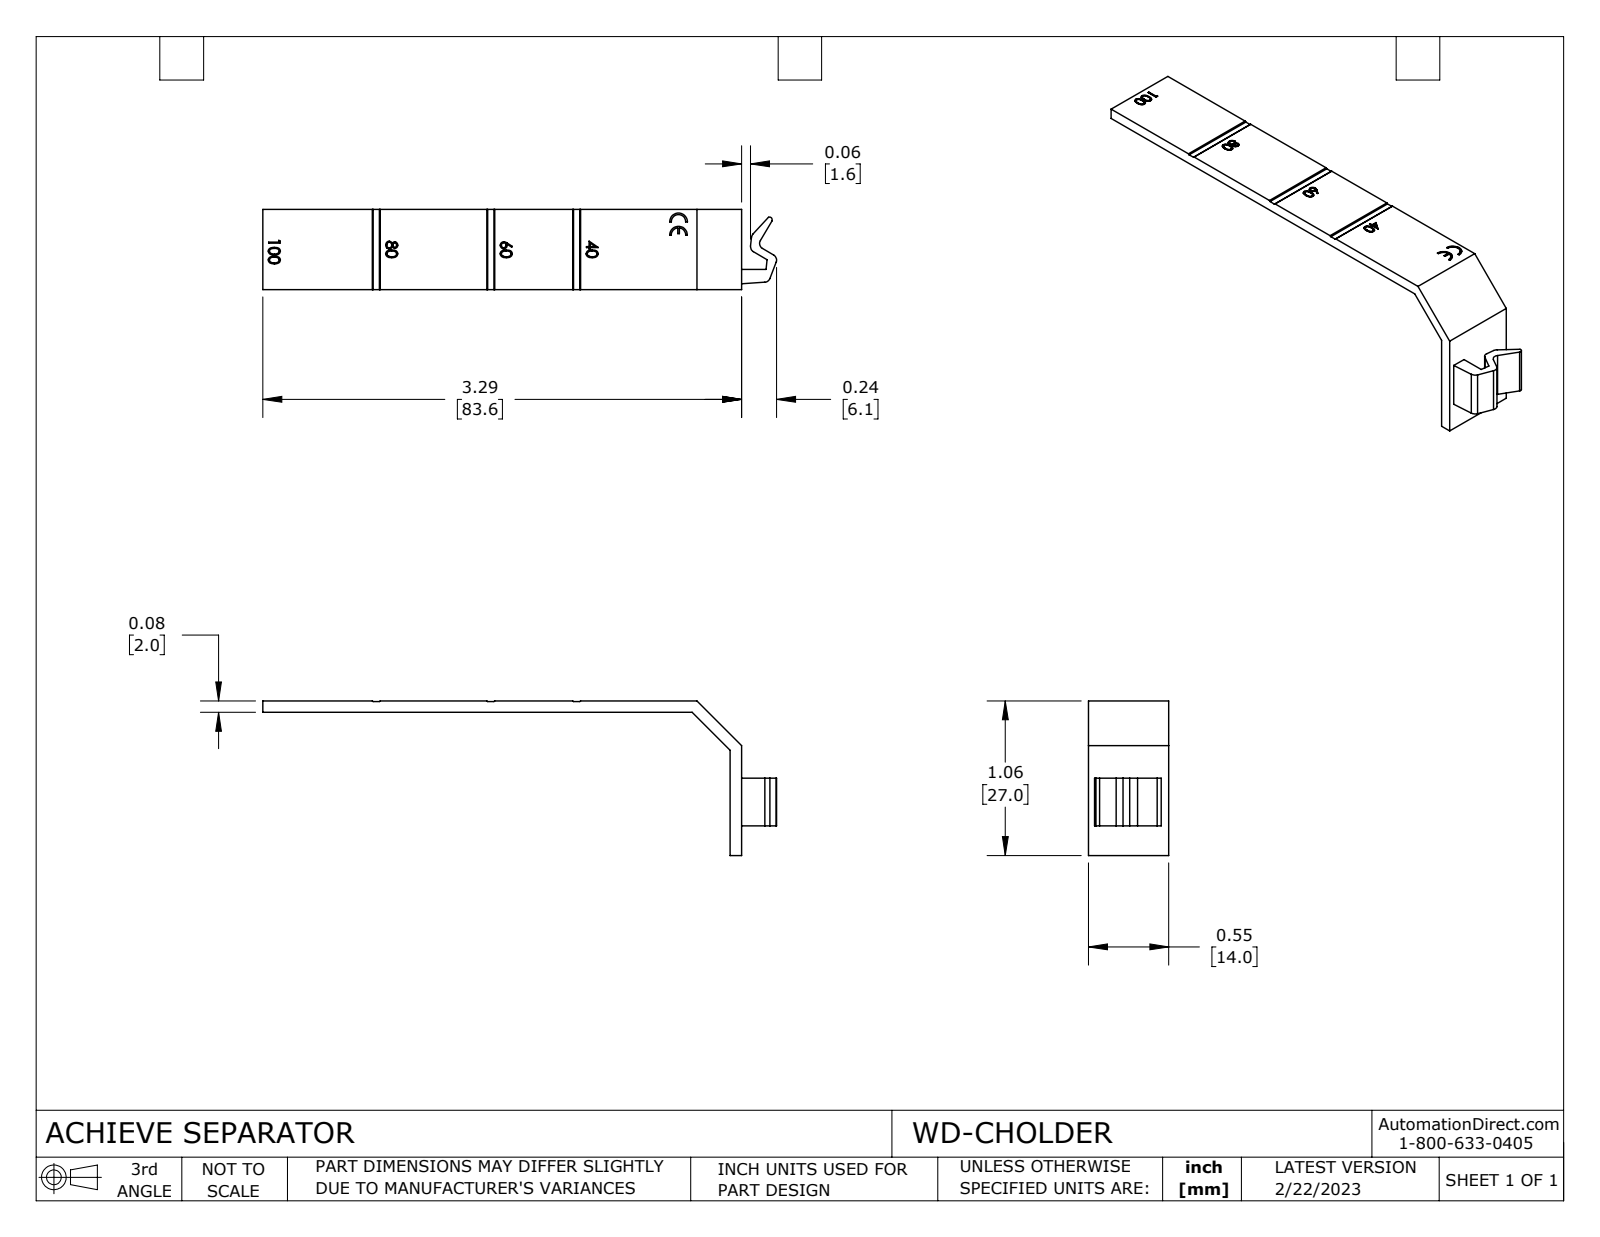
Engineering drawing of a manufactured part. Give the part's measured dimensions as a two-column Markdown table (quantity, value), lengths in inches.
| quantity | value |
| --- | --- |
| part name | WD-CHOLDER |
| STEP written by | SolidWorks 2021 (CONFIG_CONTROL_DESIGN) |
| units | inches |
| bodies | 1 solid, 164 faces (82 planar, 11 cylindrical, 71 other) |
| overall size | 3.532 × 1.063 × 0.551 |
| volume | 0.192 in³ |
| surface area | 5.784 in² |
| partial cylindrical surfaces (radius × count) | 0.039 × 5, 0.05 × 2, 0.018 × 1, 0.061 × 1, 0.061 × 1 |
| main face-to-face distances | 0.079, 0.551, 0.531, 0.074, 0.412, 0.139, 0.984, 1.058, 1.063, 3.213 |
